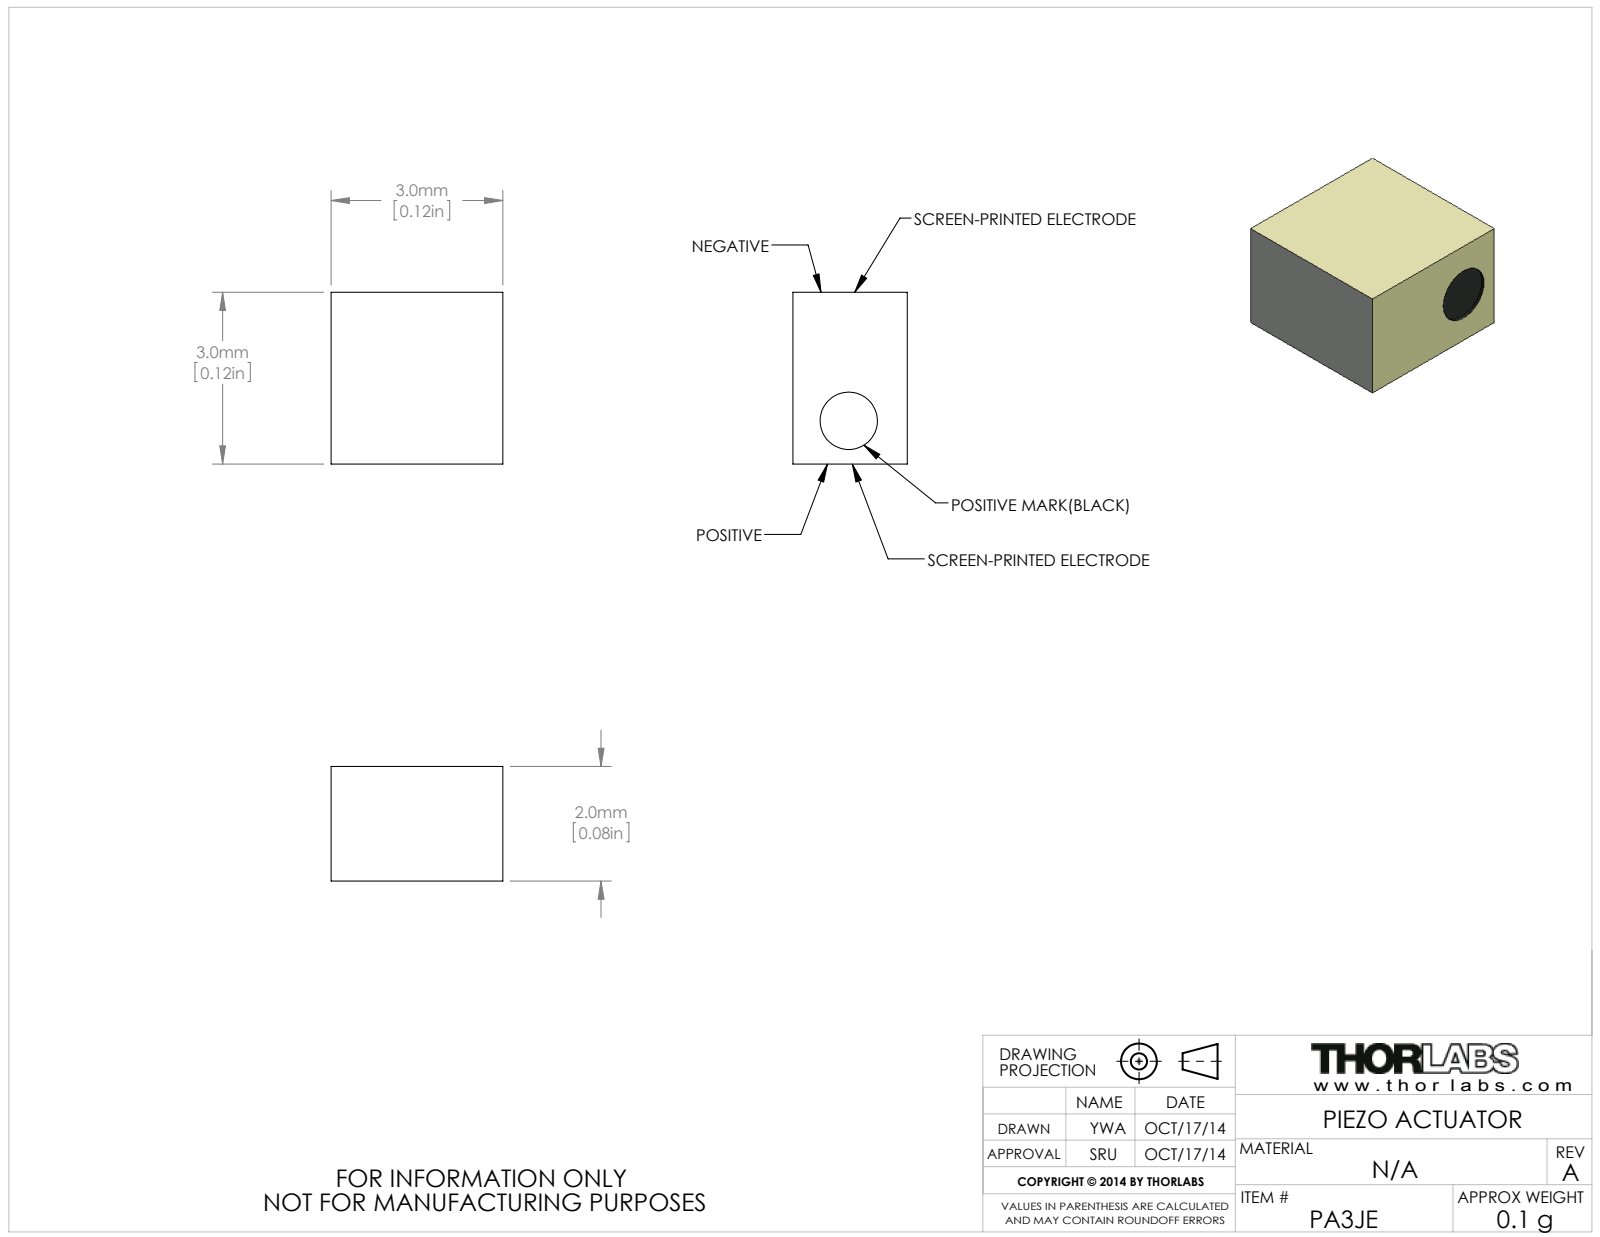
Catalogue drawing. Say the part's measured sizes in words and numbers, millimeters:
The part is named "PA3JE". Its 3-D file was written by "SolidWorks 2012 (AUTOMOTIVE_DESIGN)". It is 1 solid with 9 faces: 7 planar, 2 cylindrical and 0 other. Overall it measures 3 by 3 by 2 millimeters. Its volume is 18 cubic millimeters and its surface area 42 square millimeters. Round holes: 1 of diameter 1. The main face-to-face distances are 3, 2, 2.95.
